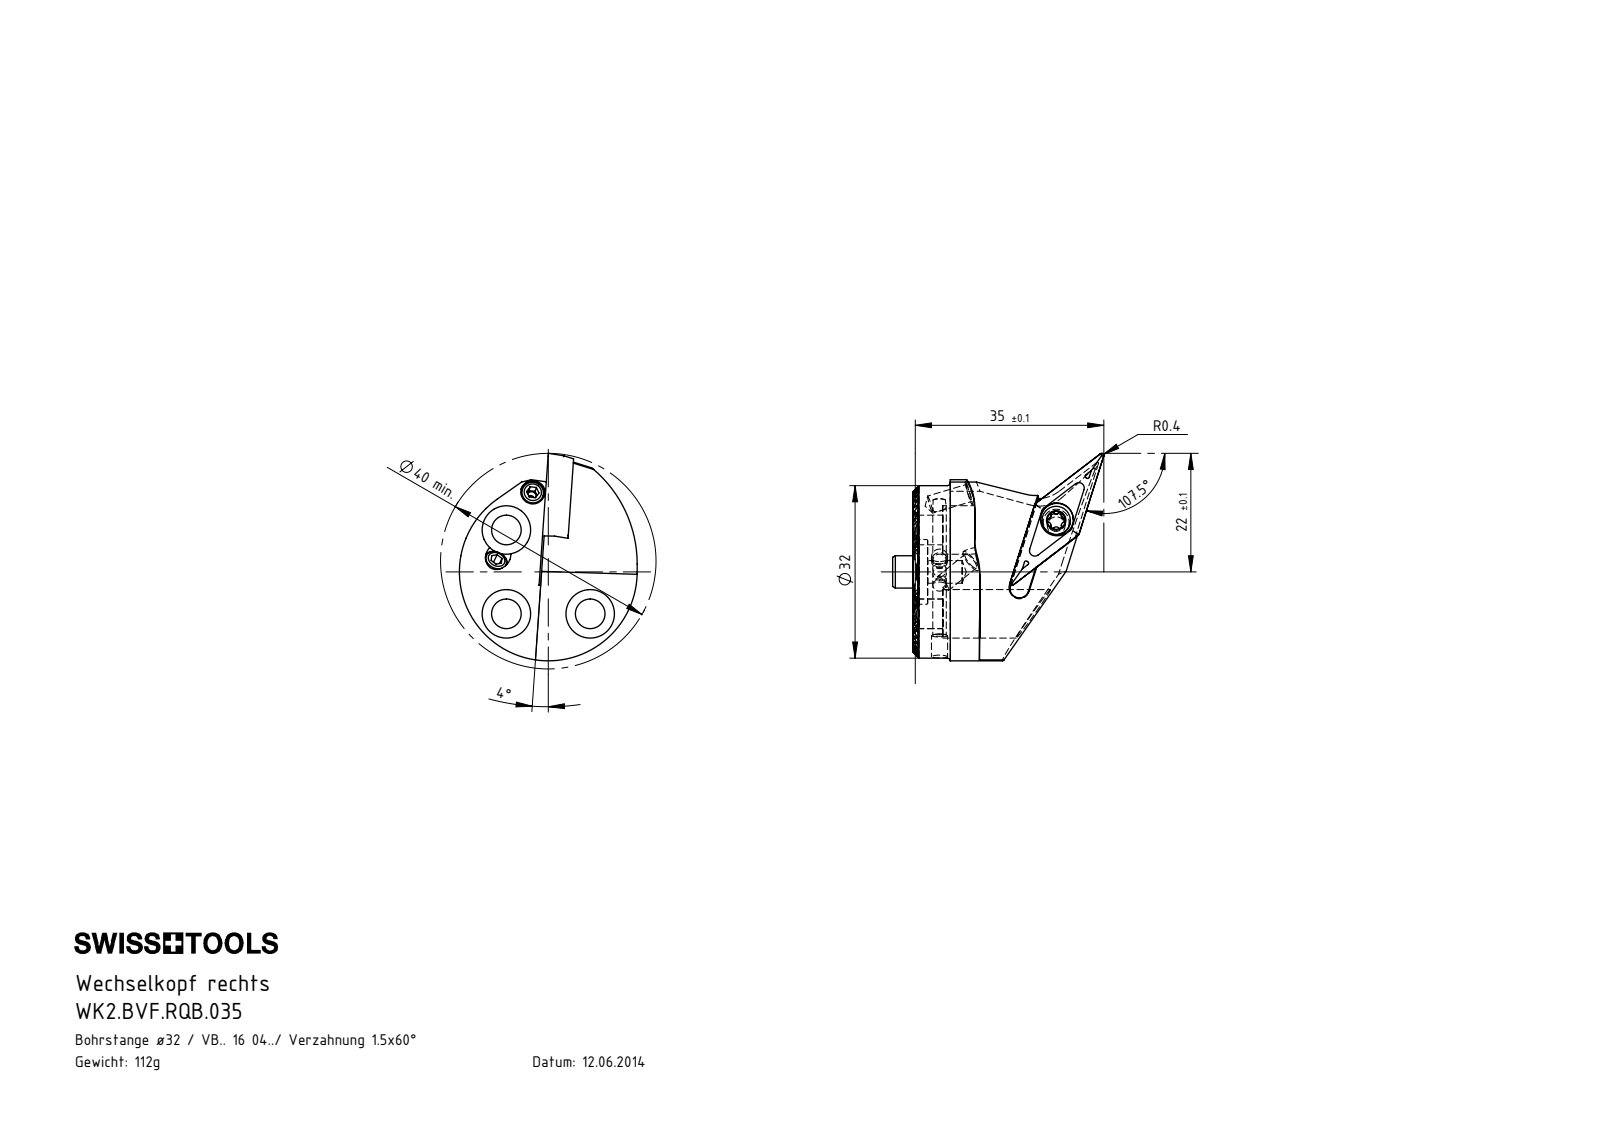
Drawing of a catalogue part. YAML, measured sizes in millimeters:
part_name: "KVT_MB_600_030; VBMT160404; WK2.BVF.RQB.035; WK2-BVF.RQB.035_A_Fertigbearbeitung (+3 more)"
step_written_by: "SolidWorks 2017 (AUTOMOTIVE_DESIGN)"
units: millimeters
bodies: {solids: 10, faces: 529, planar: 200, cylindrical: 185, other: 144}
overall_size: [39.2, 38.5, 33]
volume: 13837
surface_area: 7928
round_holes:
  - {diameter: 3.3, count: 3}
  - {diameter: 5.5, count: 3}
  - {diameter: 9, count: 3}
  - {diameter: 1.7, count: 2}
  - {diameter: 2.38, count: 2}
  - {diameter: 2.5, count: 2}
  - {diameter: 4.5, count: 2}
  - {diameter: 3, count: 1}
  - {diameter: 4.2, count: 1}
  - {diameter: 4.4, count: 1}
  - {diameter: 6.1, count: 1}
  - {diameter: 12, count: 1}
round_bosses_or_shafts:
  - {diameter: 4, count: 3}
  - {diameter: 3, count: 2}
  - {diameter: 32, count: 1}
  - {diameter: 6, count: 1}
  - {diameter: 5.25, count: 1}
partial_cylinders:
  - {radius: 0.12, count: 22}
  - {radius: 0.34, count: 6}
  - {radius: 0.59, count: 6}
  - {radius: 12, count: 3}
  - {radius: 0.15, count: 2}
  - {radius: 1.75, count: 1}
  - {radius: 7, count: 1}
  - {radius: 16.5, count: 1}
face_to_face_distances: [1.3, 2.6, 3.9, 5.2, 6.5, 12.99, 11.69, 14.29, 4.46, 7.8]
hole_center_spacings: [11, 15.56, 22.01]
